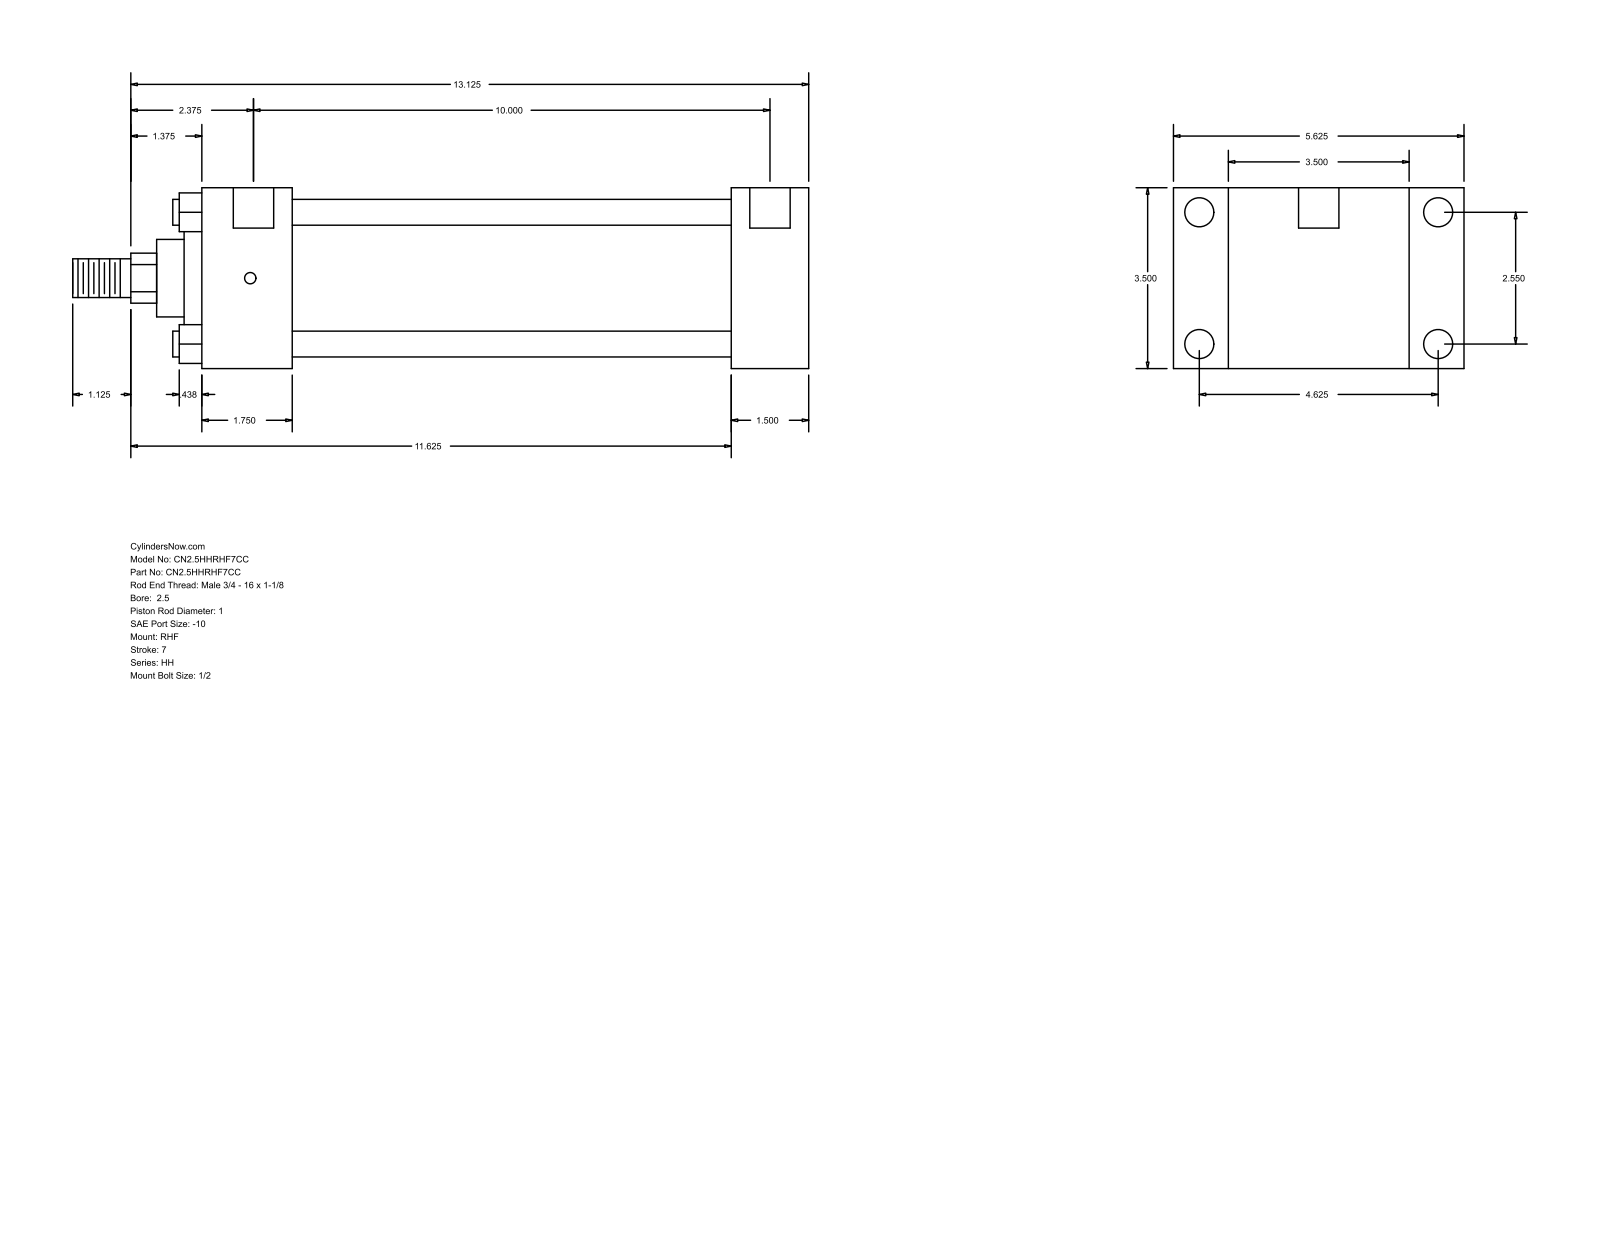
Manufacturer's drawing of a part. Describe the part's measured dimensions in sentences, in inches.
The part is named "HH_RHF__0250_1". Its 3-D file was written by "GSSL Pune (CONFIG_CONTROL_DESIGN)". It is 0 solids with 90 faces: 61 planar, 29 cylindrical and 0 other. Overall it measures 14.25 by 5.625 by 3.5 inches. Round holes: 4 of diameter 0.219, 4 of diameter 0.563, 2 of diameter 0.781. Round bosses or shafts: 4 of diameter 0.5, 1 of diameter 2.875, 1 of diameter 2.375, 1 of diameter 1.5, 1 of diameter 1, 1 of diameter 0.75. Partial cylindrical surfaces (rounded edges, fillets, slot ends): 1 of radius 0.484. The main face-to-face distances are 3.5, 1.5, 1.063, 4.563, 10.25, 11.75, 5.625, 1.75, 8.5, 10. The hole center spacings are 0.063, 2.55, 4.625, 5.281, 10.062, 10.125, 10.
